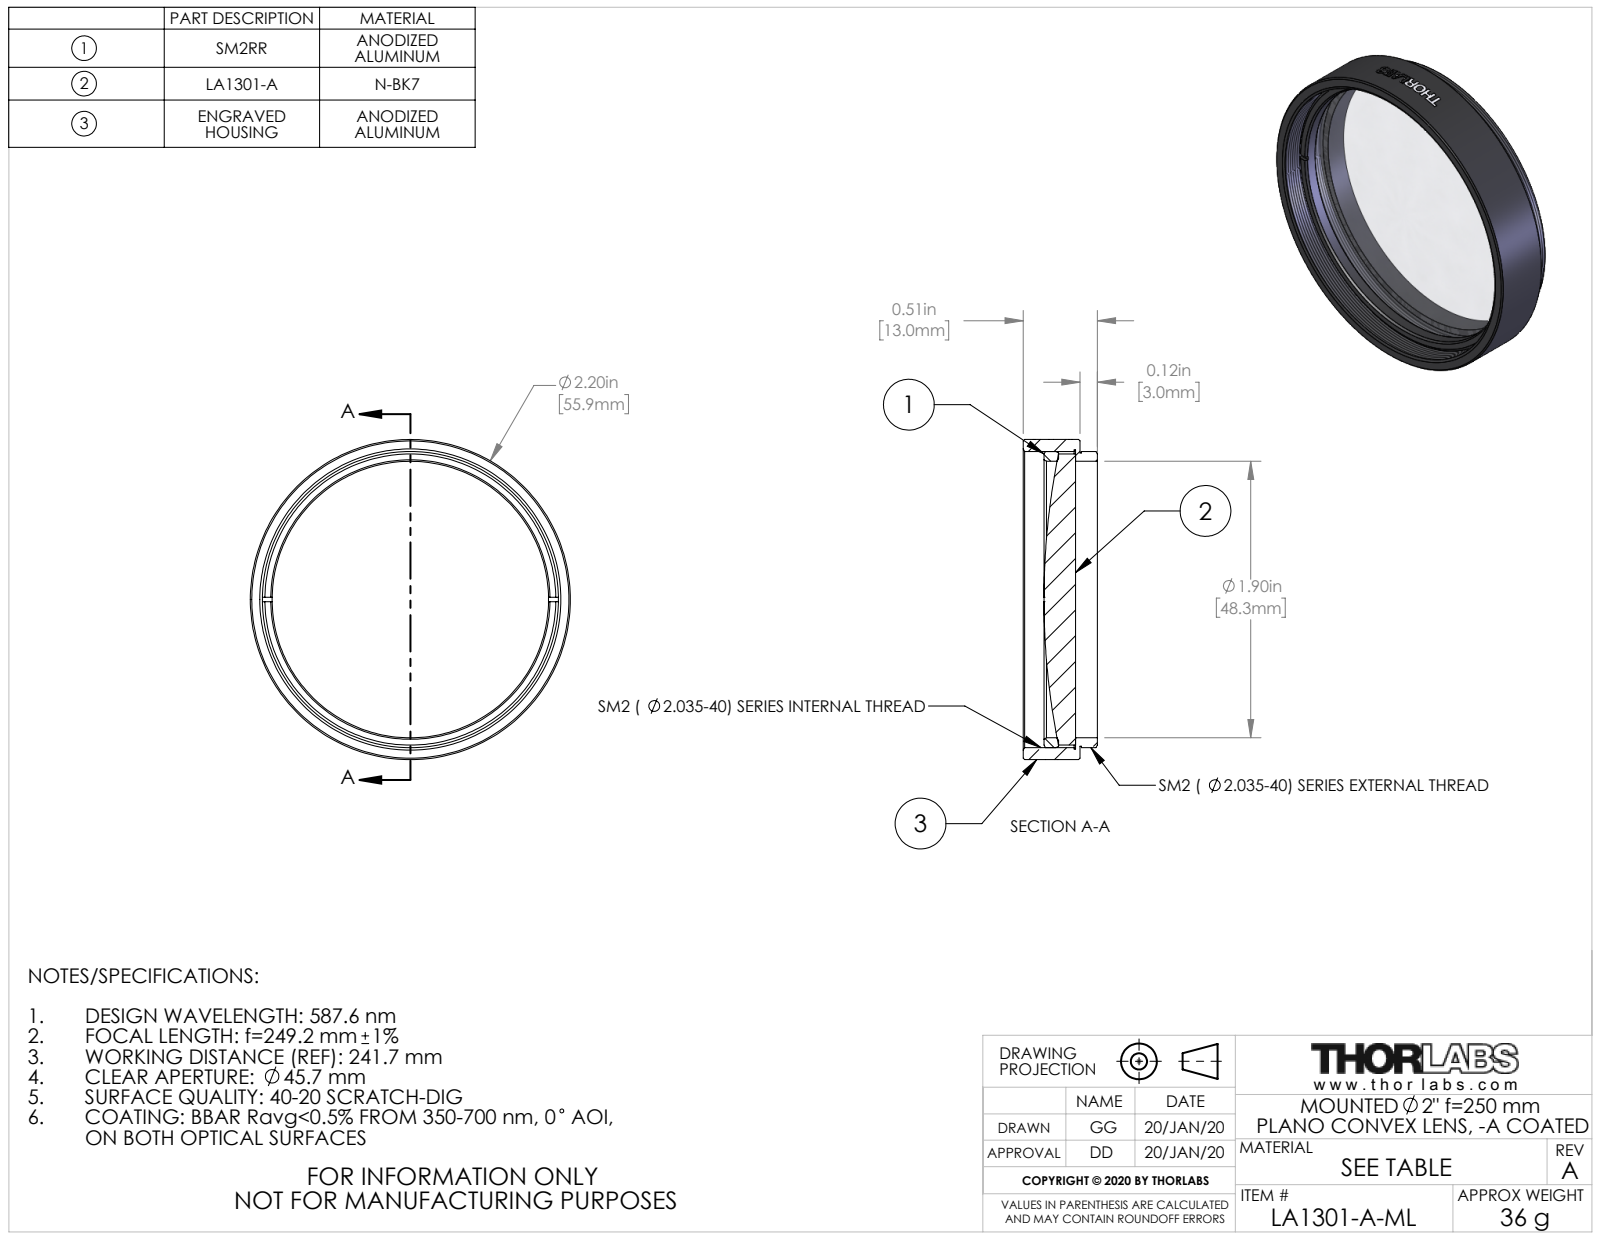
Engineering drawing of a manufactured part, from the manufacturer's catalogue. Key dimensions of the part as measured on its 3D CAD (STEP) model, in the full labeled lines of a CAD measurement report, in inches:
Part name (STEP PRODUCT): TTN203752-E0W
STEP written by: SolidWorks 2018 (CONFIG_CONTROL_DESIGN)
Units: inches
Bodies: 3 solids, 146 faces (16 planar, 110 cylindrical, 20 other)
Overall size (bounding box): 2.2 × 2.2 × 0.51
Volume: 0.84 in³ · Surface area: 17.62 in²
Round holes (diameter × count): ⌀1.9 ×1, ⌀2.055 ×1
Round bosses / shafts (diameter × count): ⌀2.2 ×1, ⌀2.035 ×1, ⌀2.015 ×1, ⌀2 ×1
Main face-to-face distances: 0.03, 0.39, 0.36, 0.12, 0.15, 0.51, 0.268, 0.148, 0.118, 0.243
